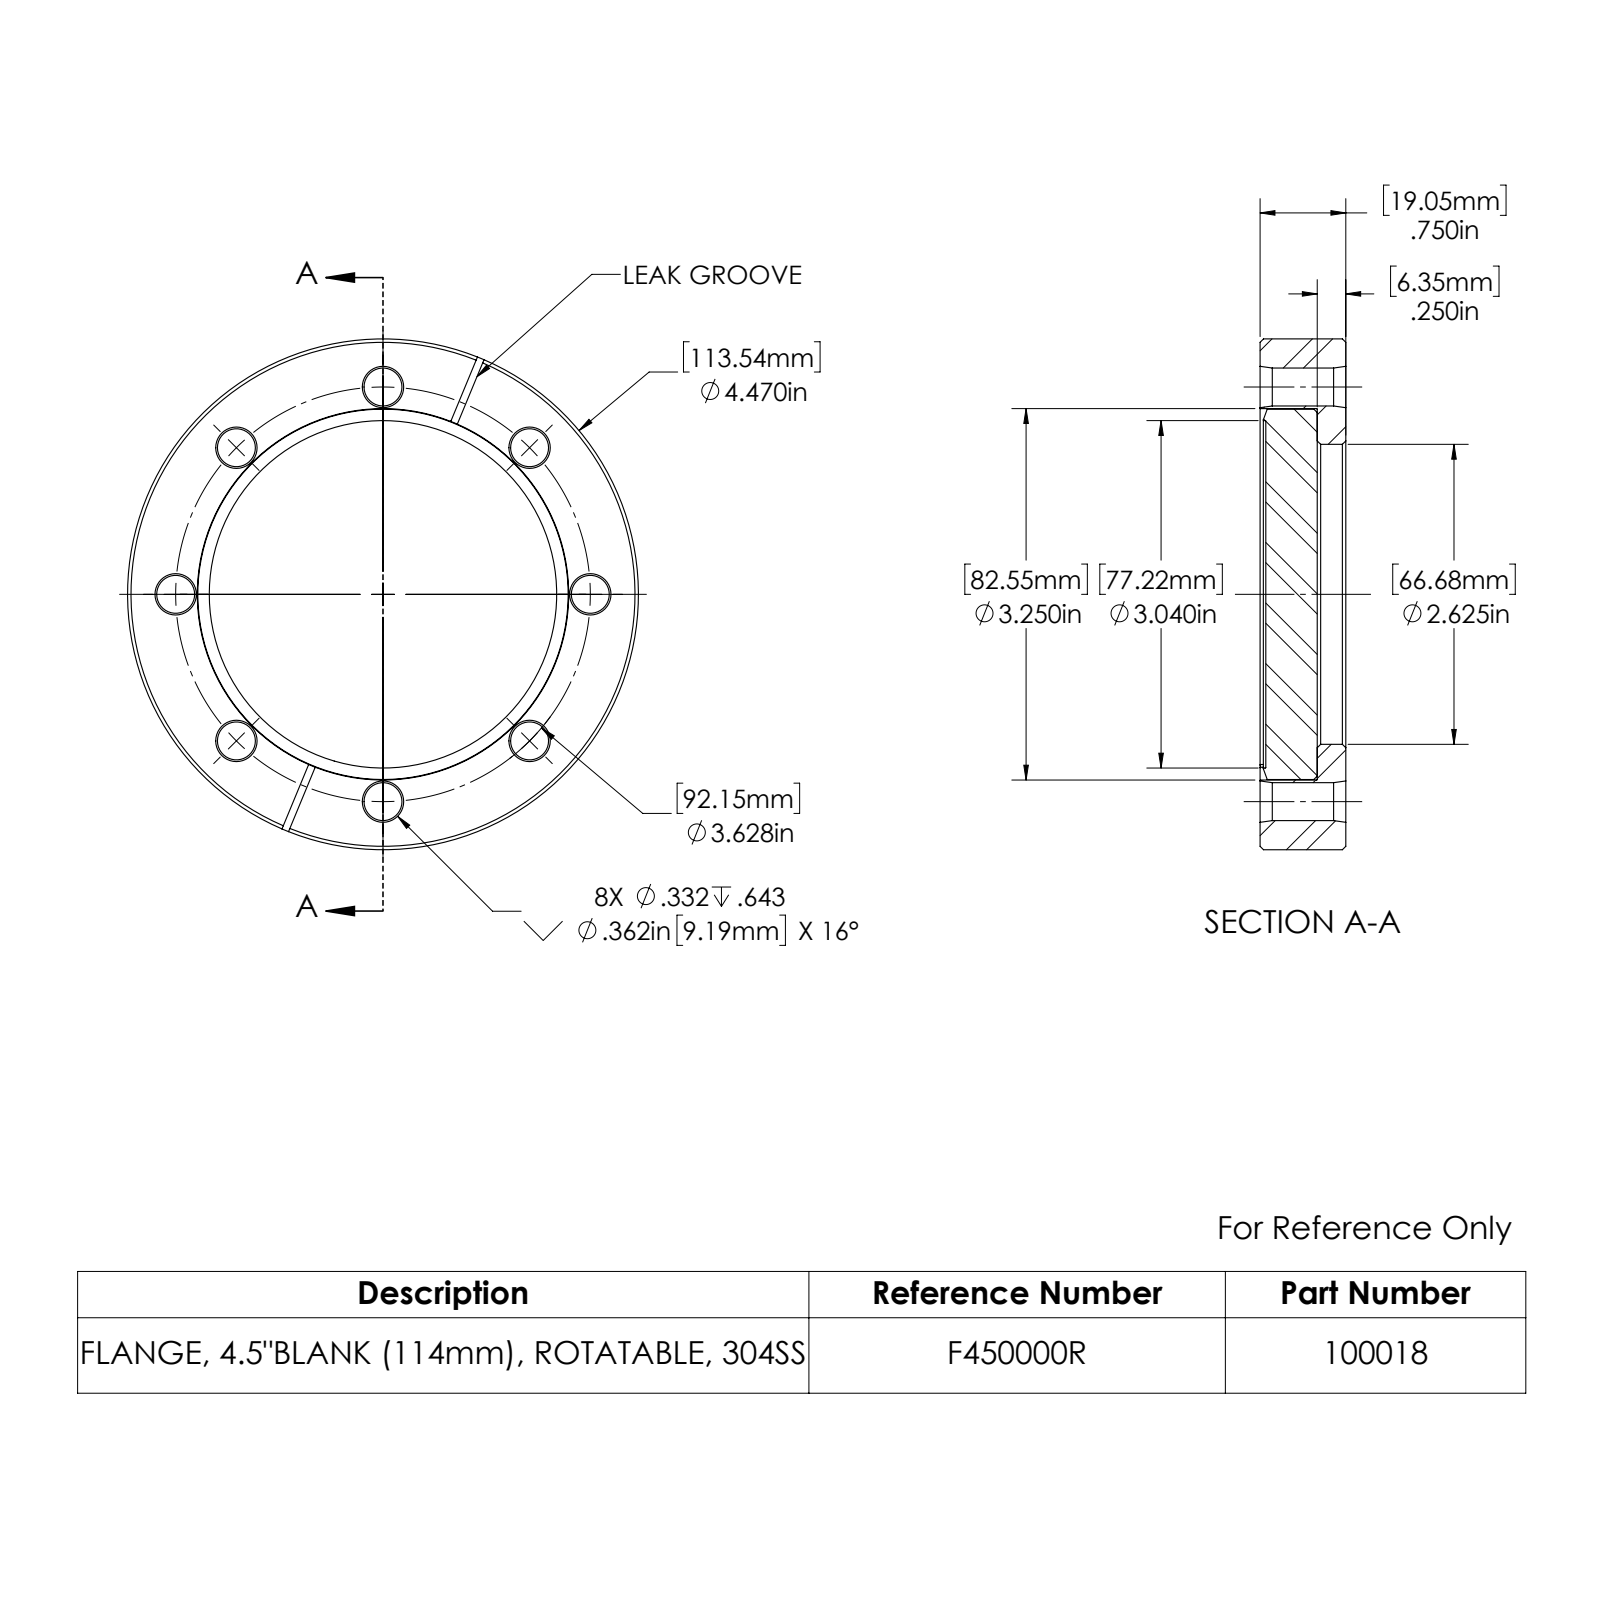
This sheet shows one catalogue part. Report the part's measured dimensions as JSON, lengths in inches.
{"part_name": "915004; 100018_A; 910018", "step_written_by": "SolidWorks 2022 (CONFIG_CONTROL_DESIGN)", "units": "inches", "bodies": {"solids": 2, "faces": 92, "planar": 12, "cylindrical": 26, "other": 54}, "overall_size": [4.47, 4.47, 0.75], "volume_in3": 9.424, "surface_area_in2": 63.28, "round_holes": [[0.332, 8], [2.625, 1], [3.04, 1], [3.25, 1]], "round_bosses_or_shafts": [[4.47, 1], [3.241, 1]], "face_to_face_distances": [0.25, 0.45, 0.7, 0.05, 0.5, 0.75, 0.062, 0.012, 0.438, 0.688], "hole_center_spacings": [1.814, 2.565, 1.388, 1.389, 3.352, 3.352, 3.628, 1.814]}
